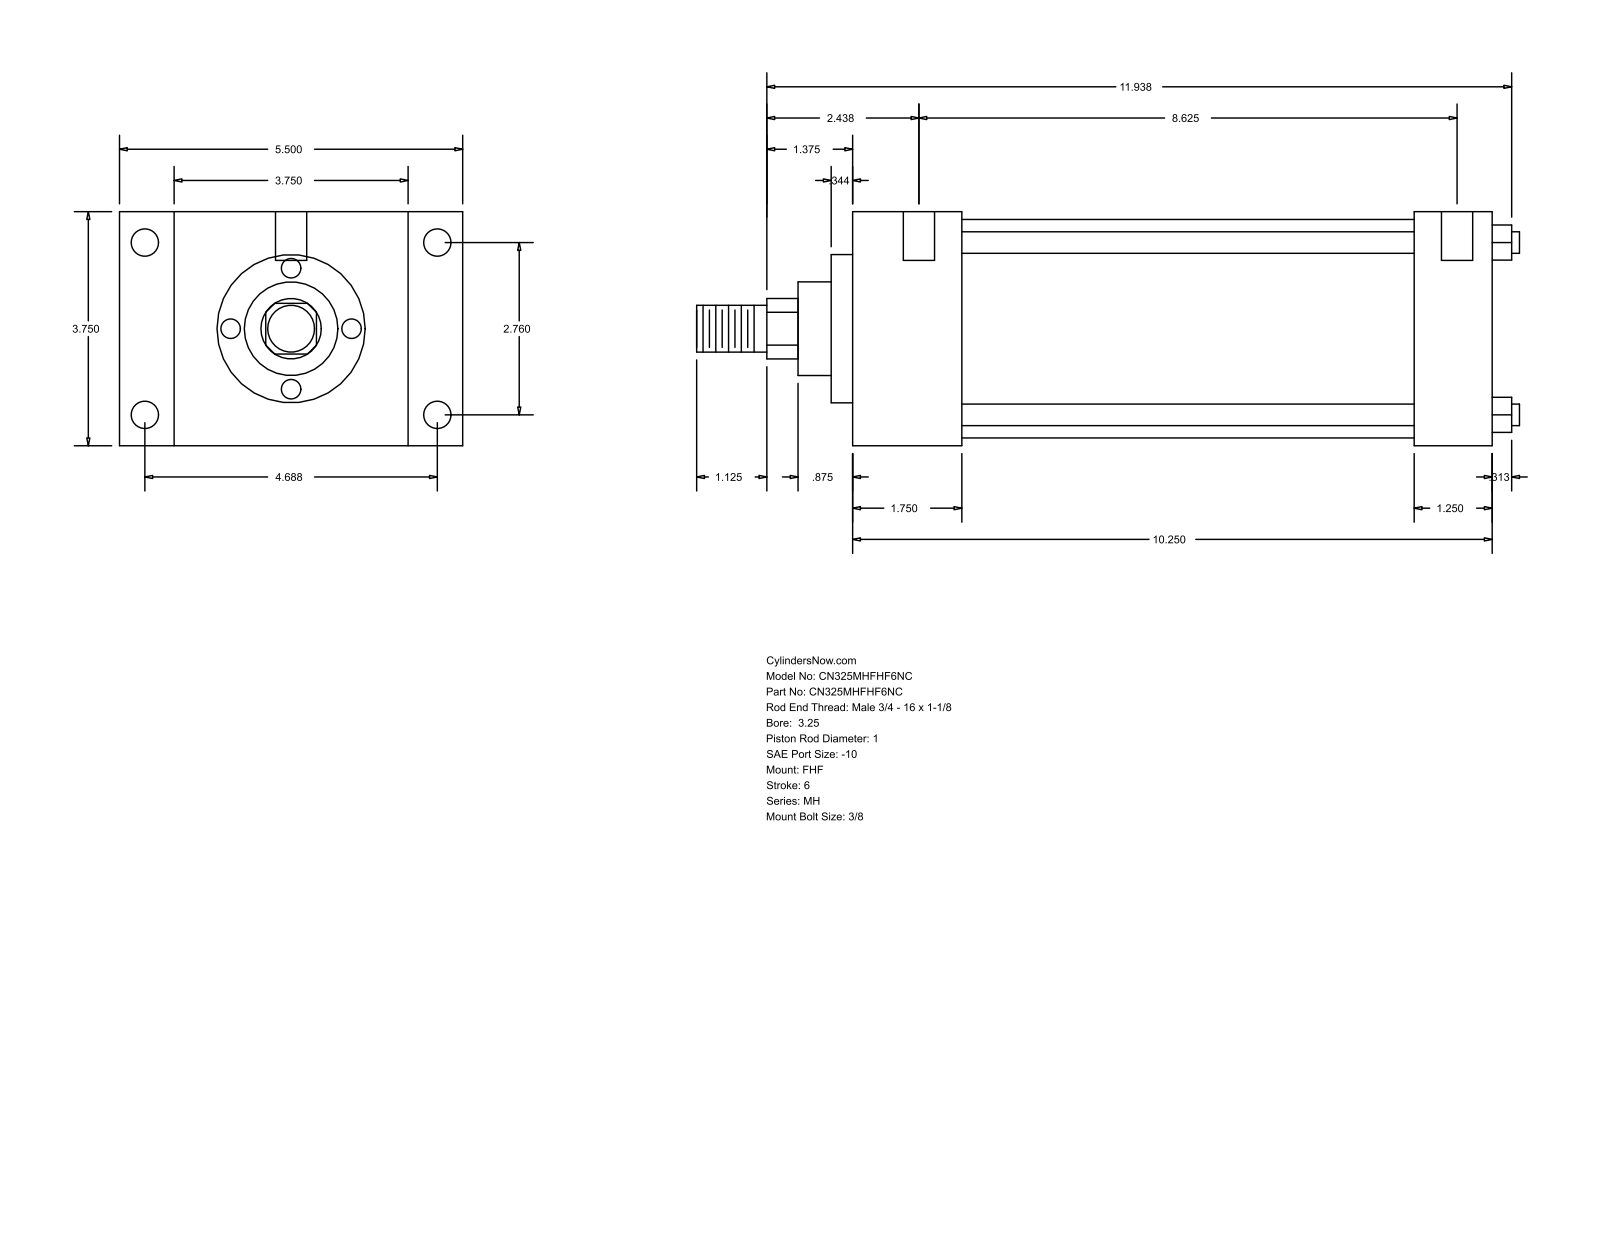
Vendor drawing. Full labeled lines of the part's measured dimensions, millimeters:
Part name (STEP PRODUCT): MH_FHF__0325_1
STEP written by: GSSL Pune (CONFIG_CONTROL_DESIGN)
Units: millimetres
Bodies: 0 solids, 90 faces (61 planar, 29 cylindrical, 0 other)
Overall size (bounding box): 334.96 × 139.7 × 95.25
Round holes (diameter × count): ⌀5.56 ×4, ⌀11.13 ×4, ⌀12.7 ×2
Round bosses / shafts (diameter × count): ⌀8.76 ×4, ⌀88.9 ×1, ⌀60.33 ×1, ⌀38.1 ×1, ⌀25.4 ×1, ⌀19.05 ×1
Partial cylindrical surfaces — rounded edges, fillets, slot ends (radius × count): R12.29 ×1
Main face-to-face distances: 95.24, 260.35, 44.46, 215.89, 22.23, 117.47, 139.7, 228.6, 184.14, 31.75
Hole centre spacings: 70.1, 119.06, 138.16, 225.42, 1.58, 4.76, 219.08, 220.66
